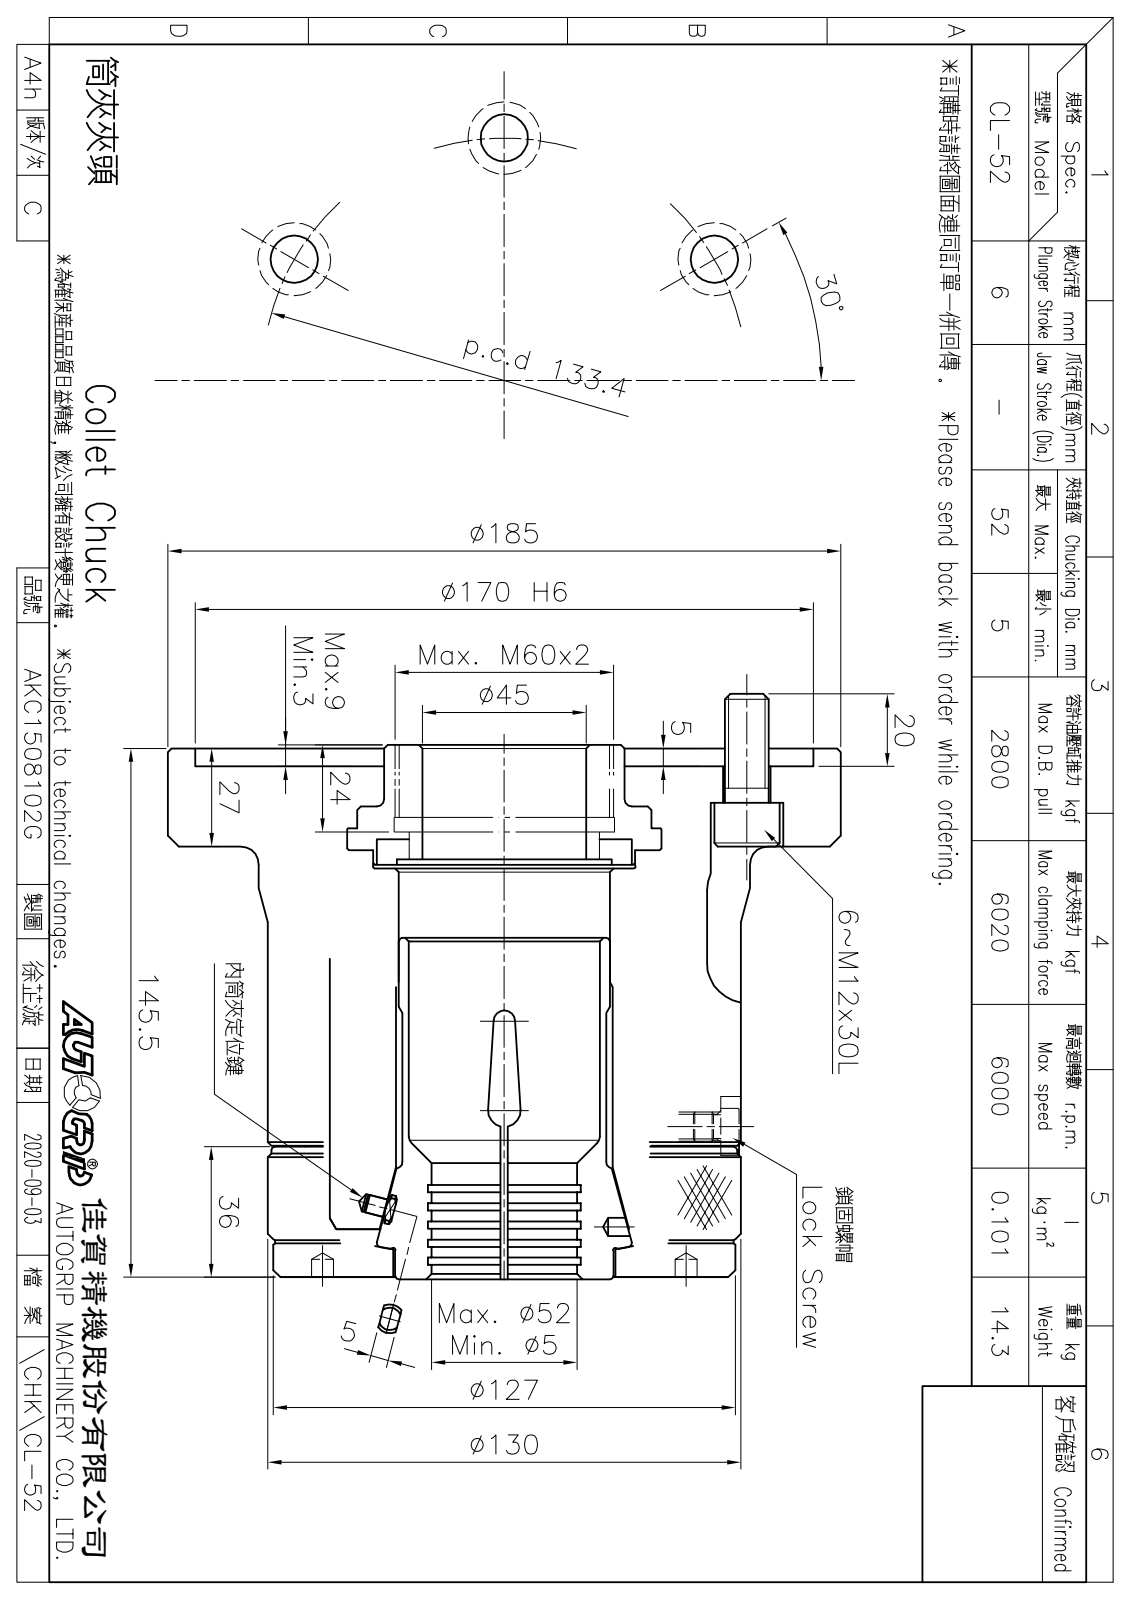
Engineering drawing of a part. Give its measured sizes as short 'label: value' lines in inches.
name: CF-CL-52-02000; CF-CL-6017-01010; CF-CL-52; 圓頭內六角螺栓_M12x30 (+4 more)
written by: SolidWorks 2016 (CONFIG_CONTROL_DESIGN)
unit: in
bodies: 12 solids, 455 faces (142 planar, 152 cylindrical, 161 other)
size: 7.283 × 7.283 × 6.311
volume: 103.3 in³; area: 460.4 in²
holes: 6× ⌀0.531, 6× ⌀0.787, 2× ⌀0.236, 1× ⌀0.197, 1× ⌀0.268, 1× ⌀2.059, 1× ⌀2.283, 1× ⌀2.323, 1× ⌀2.343, 1× ⌀2.382, 1× ⌀2.402, 1× ⌀2.835
bosses: 6× ⌀0.709, 6× ⌀0.472, 1× ⌀7.283, 1× ⌀5.118, 1× ⌀5.039, 1× ⌀5, 1× ⌀4.961, 1× ⌀4.311
rounds: 6× R0.394, 3× R0.335, 1× R0.157, 1× R0.315, 1× R0.325, 1× R2.657
face distances: 4.106, 0.787, 0.866, 0.079, 1.417, 3.24, 0.197, 5.524, 4.657, 0.472
hole spacings: 2.626, 1.348, 3.282, 4.548, 1.969, 4.441, 4.441, 4.548
